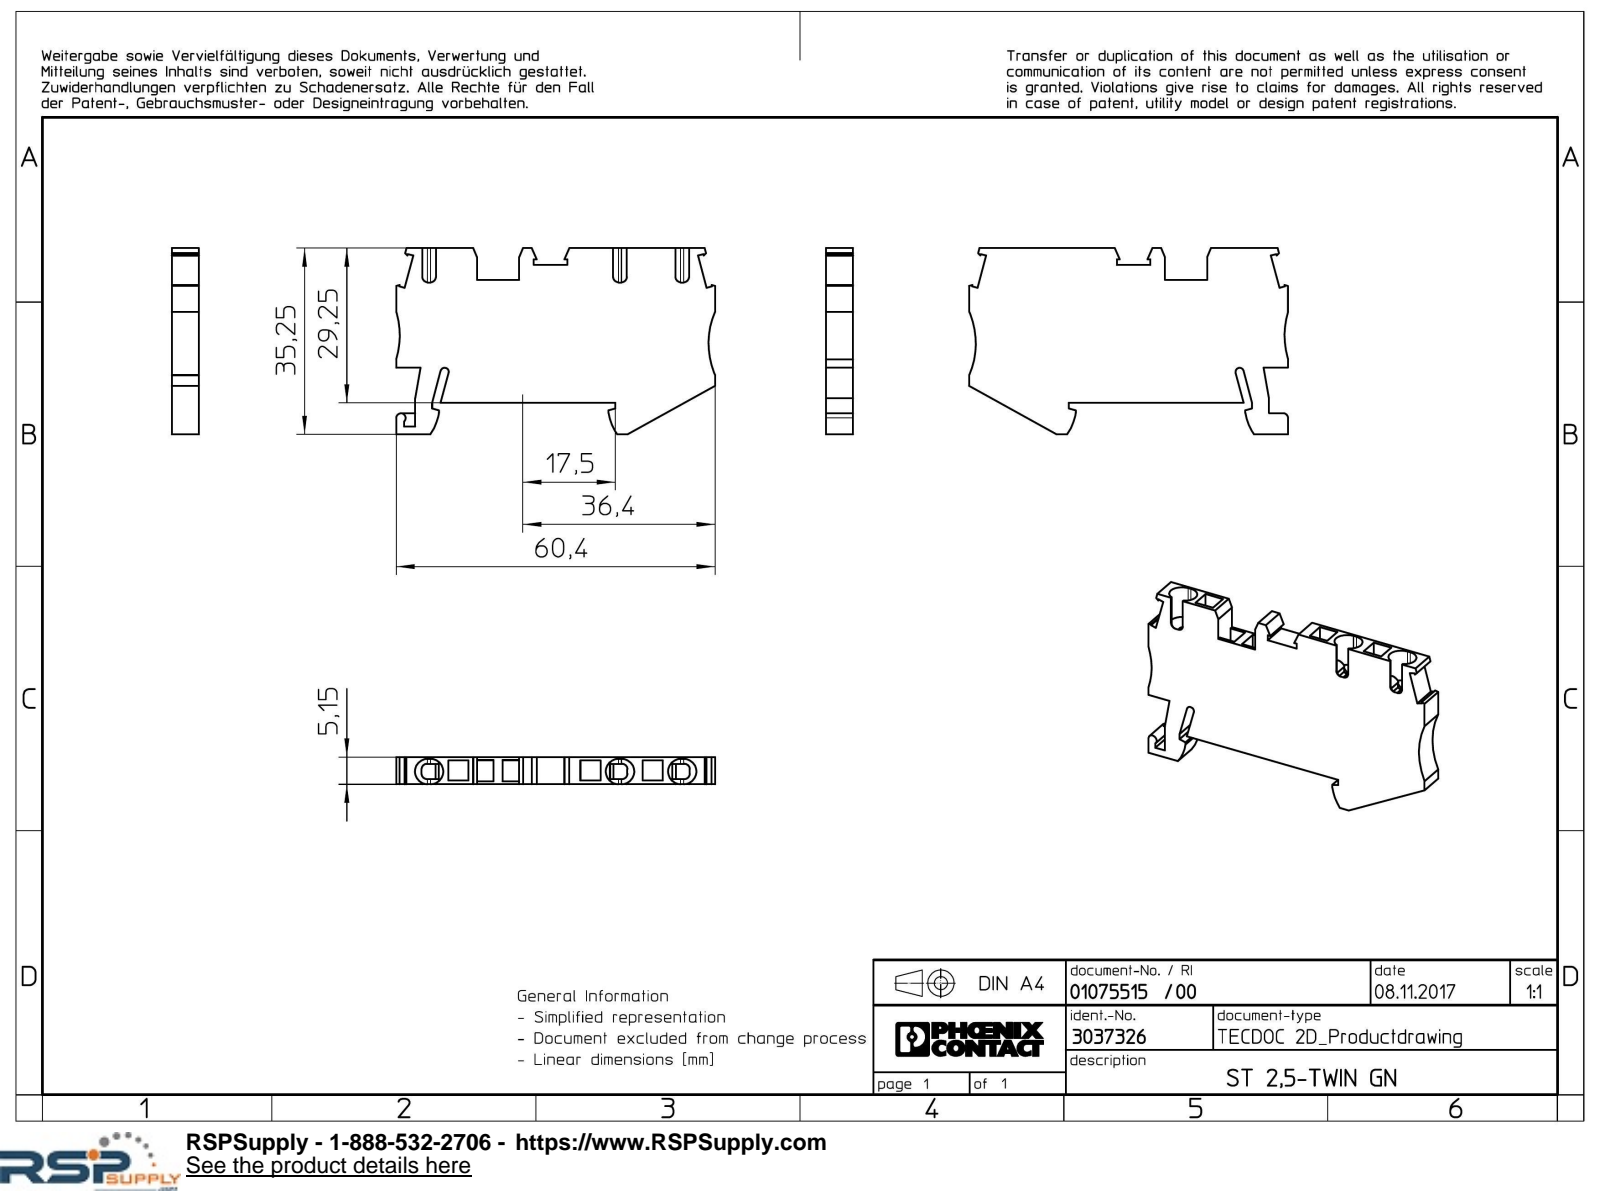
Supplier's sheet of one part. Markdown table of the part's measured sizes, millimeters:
| quantity | value |
| --- | --- |
| part name | ST_25_TWIN_GN_select |
| STEP written by | Creo Elements/Direct Modeling 20.1A 29-Sep-2018 (C) Parametric Technology GmbH (AUTOMOTIVE_DESIGN) |
| units | millimeters |
| bodies | 1 solid, 153 faces (119 planar, 25 cylindrical, 9 other) |
| overall size | 60.4 × 35.25 × 5.15 |
| volume | 7 460 mm³ |
| surface area | 5 794 mm² |
| partial cylindrical surfaces (radius × count) | 1 × 12, 2.4 × 6, 9.5 × 2, 15 × 2, 0.7 × 1, 0.8 × 1, 0.9 × 1 |
| main face-to-face distances | 5.15, 3.15, 3.8, 0.65, 29.25, 4.85, 4.45, 8, 4, 3.85 |
